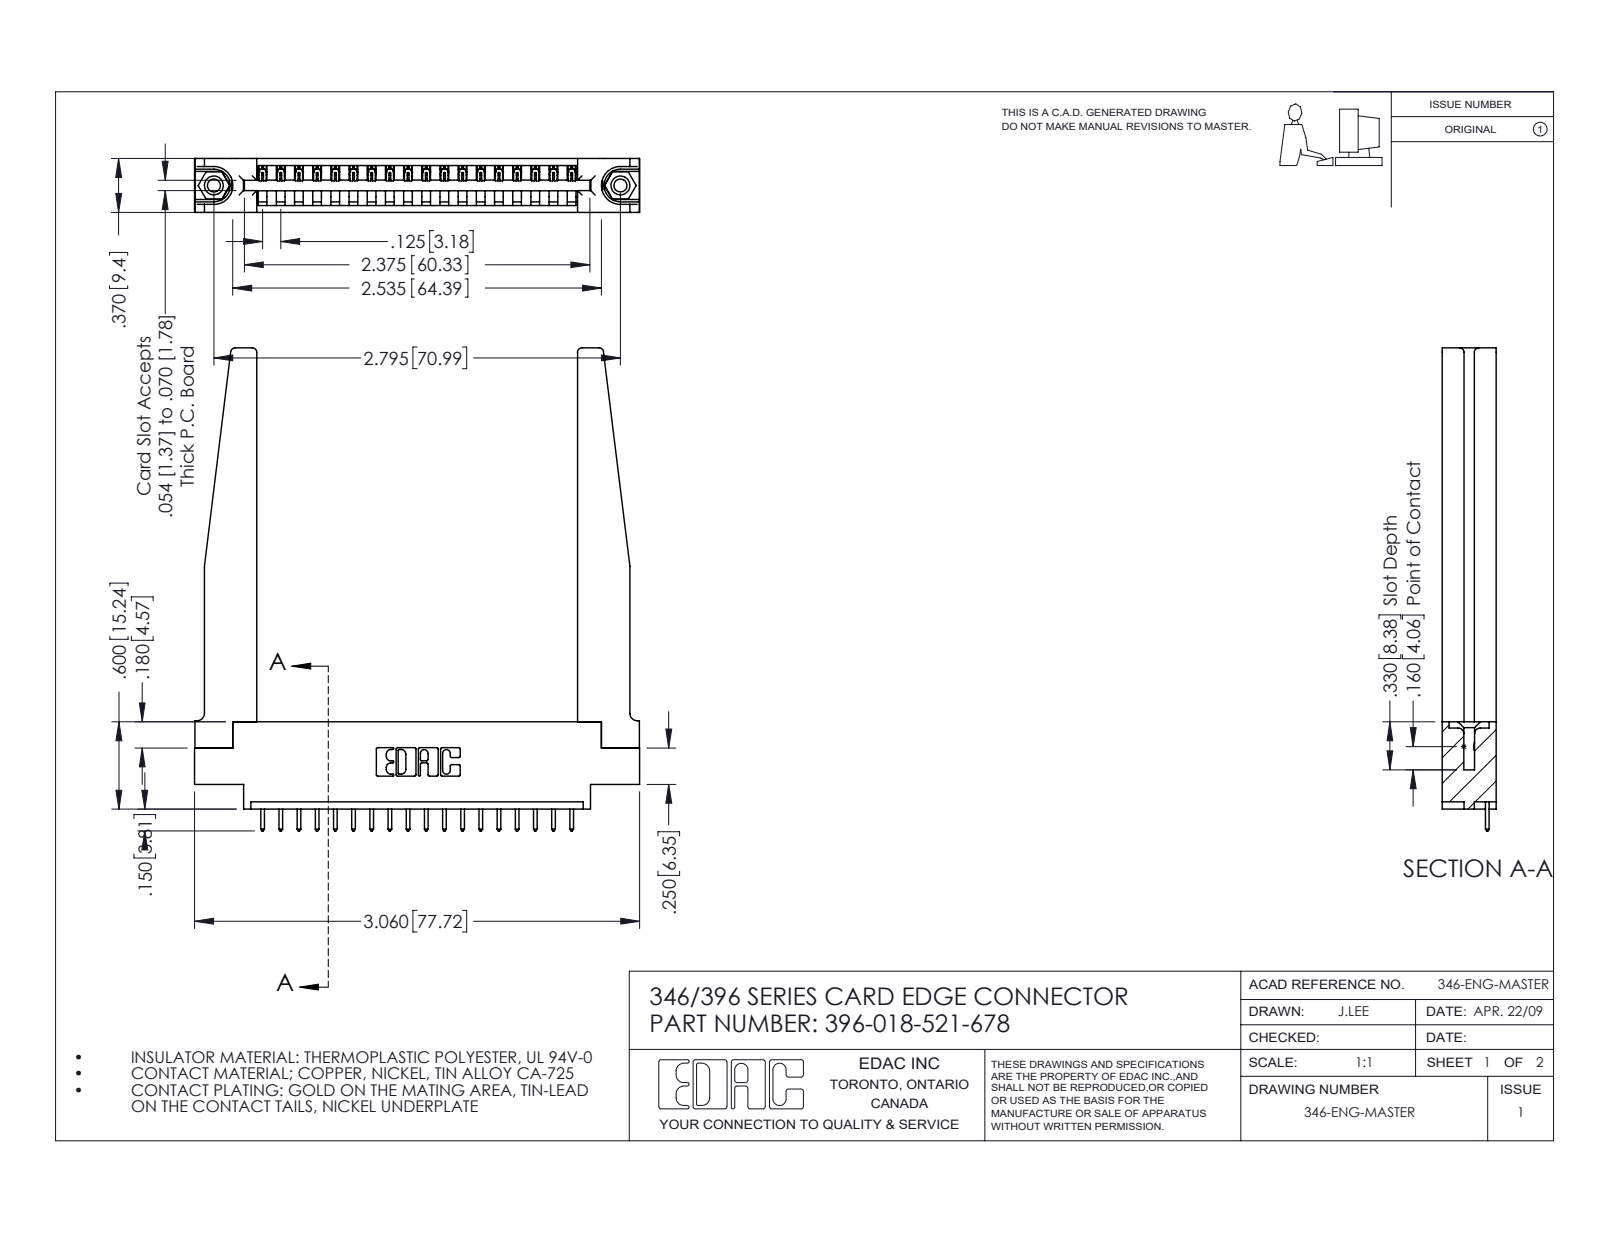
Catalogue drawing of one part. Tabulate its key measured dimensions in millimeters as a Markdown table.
| quantity | value |
| --- | --- |
| part name | 345-292-001_345-293-121; 346 Part_0.170 Offset - 0.156 Dia-TH; 345-250-001_345-250-001-102; 346-220-078_345-220-078 (+1 more) |
| STEP written by | SolidWorks 2016 (CONFIG_CONTROL_DESIGN) |
| units | millimeters |
| bodies | 23 solids, 1404 faces (942 planar, 410 cylindrical, 52 other) |
| overall size | 84.3 × 77.7 × 9.4 |
| volume | 14 000 mm³ |
| surface area | 15 070 mm² |
| round holes (diameter × count) | 2.3 × 2, 3.2 × 2, 4 × 2, 1.6 × 1 |
| round bosses / shafts (diameter × count) | 3.9 × 2 |
| partial cylindrical surfaces (radius × count) | 0.2 × 36, 0.3 × 36, 0.3 × 22, 0.8 × 8, 0.2 × 6, 0.8 × 6, 0.7 × 3, 0.8 × 2 |
| main face-to-face distances | 9.4, 1.8, 3.8, 3.8, 1.2, 8.2, 6.4, 2.6, 5.6, 4.4 |
| hole center spacings | 6.2, 65.7, 71 |
